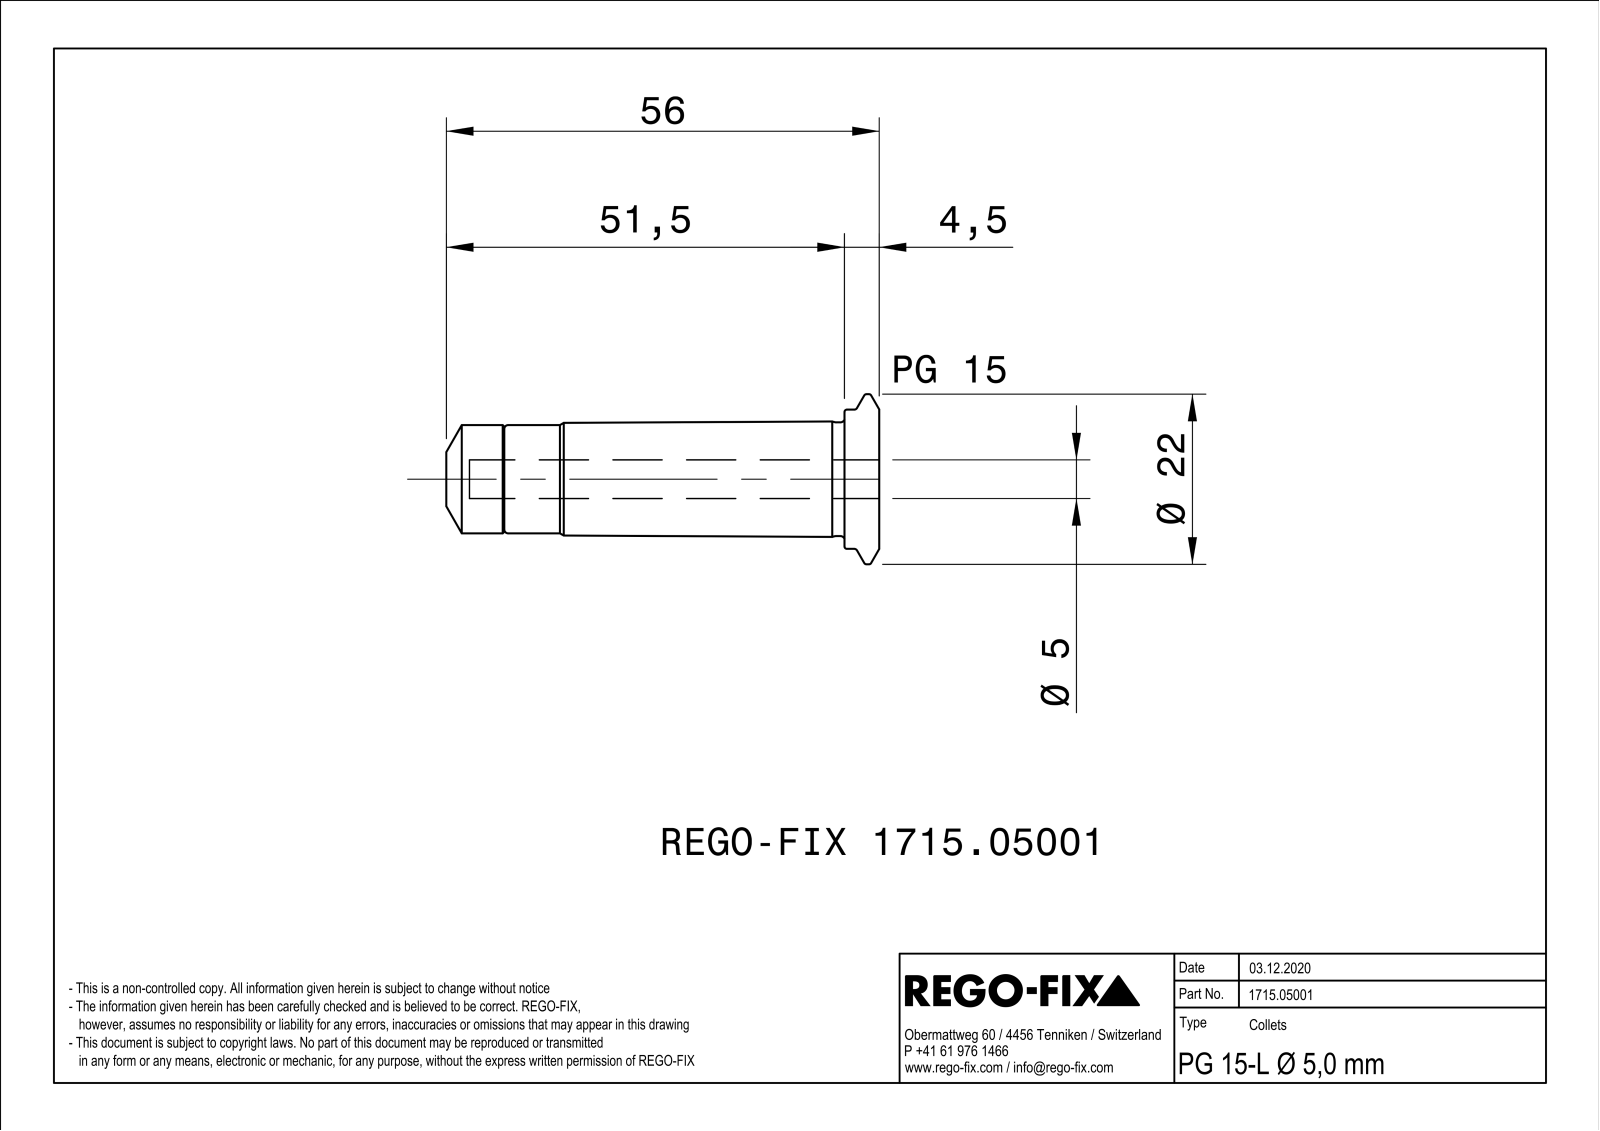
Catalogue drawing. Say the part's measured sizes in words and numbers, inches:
The part is named "0016413". Its 3-D file was written by "ST-DEVELOPER v16.7 (AUTOMOTIVE_DESIGN)". It is 1 solid with 97 faces: 24 planar, 28 cylindrical and 45 other. Overall it measures 2.205 by 0.866 by 0.866 inches. Its volume is 0.049 cubic inches and its surface area 8.905 square inches. Round holes: 1 of diameter 0.11, 1 of diameter 0.197, 1 of diameter 0.335, 1 of diameter 0.362, 1 of diameter 0.43, 1 of diameter 0.48. Round bosses or shafts: 1 of diameter 0.866, 1 of diameter 0.709, 1 of diameter 0.579, 1 of diameter 0.551, 1 of diameter 0.472, 1 of diameter 0.409. Partial cylindrical surfaces (rounded edges, fillets, slot ends): 6 of radius 0.02, 3 of radius 0.079. The main face-to-face distances are 0.039, 1.909, 0.295, 2.205, 2.028, 1.732, 0.177, 0.52, 0.224, 1.508.
